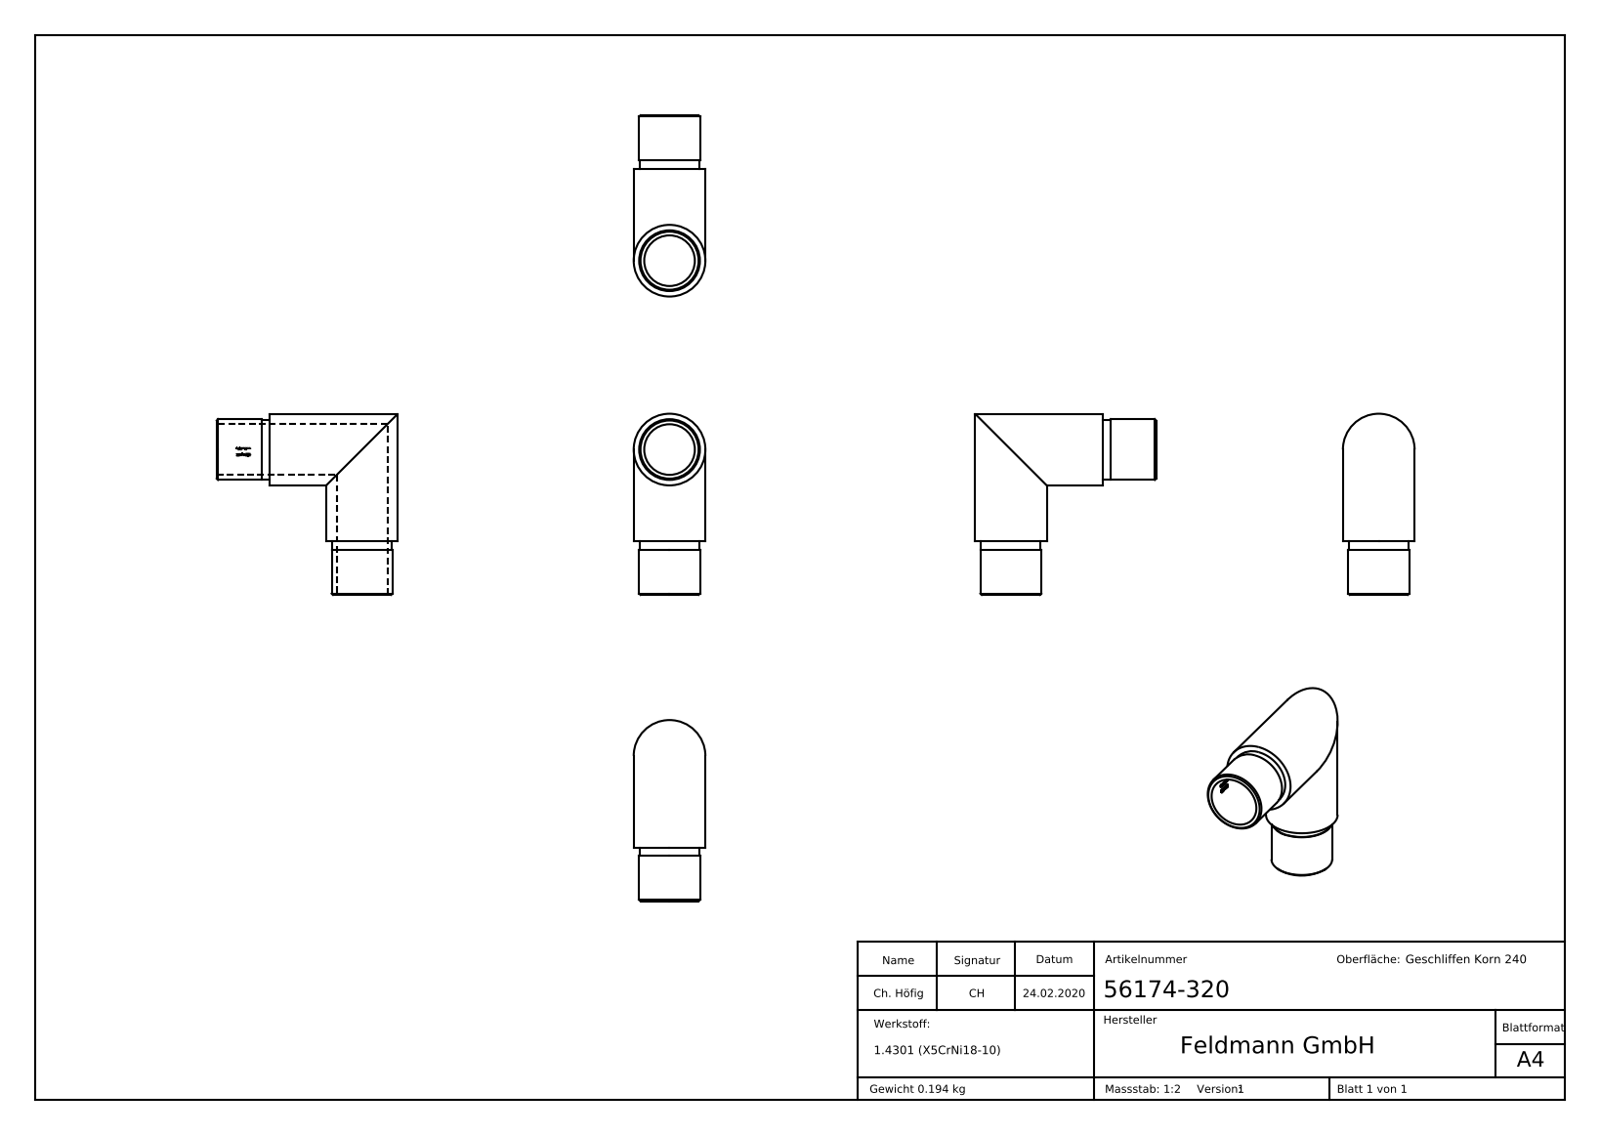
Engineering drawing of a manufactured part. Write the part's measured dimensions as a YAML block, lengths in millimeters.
part_name: "56174-320"
step_written_by: "SolidWorks 2015 (CONFIG_CONTROL_DESIGN)"
units: millimeters
bodies: {solids: 1, faces: 234, planar: 107, cylindrical: 31, other: 96}
overall_size: [68, 68, 26.9]
volume: 24566
surface_area: 15799
round_holes:
  - {diameter: 19, count: 2}
round_bosses_or_shafts:
  - {diameter: 26.9, count: 2}
  - {diameter: 22.8, count: 2}
  - {diameter: 22.4, count: 2}
partial_cylinders:
  - {radius: 9.6, count: 1}
face_to_face_distances: [20, 17, 3, 0.83, 1.78, 0.53, 0.76, 2.45, 2.61, 1.21]
